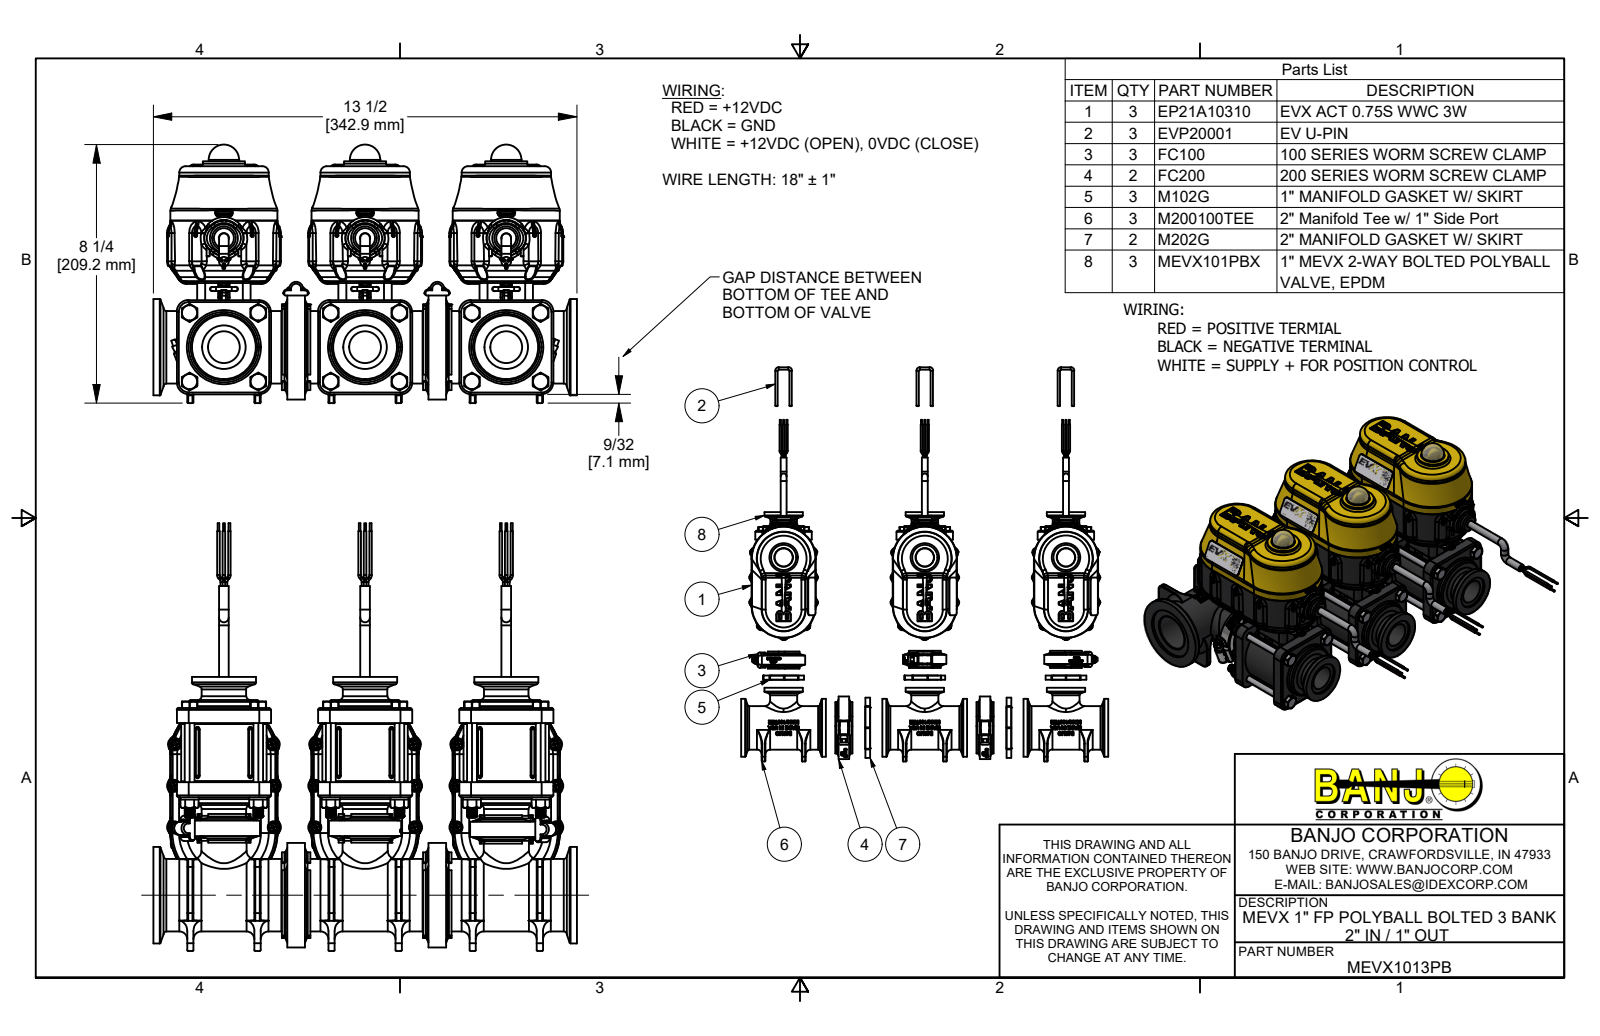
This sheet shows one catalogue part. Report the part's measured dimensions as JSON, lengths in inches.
{"part_name": "MEVX1013PB; EP21A10310; EP10310; IRF4905 (+8 more)", "step_written_by": "Autodesk Inventor 2022 (AUTOMOTIVE_DESIGN)", "units": "inches", "bodies": {"solids": 301, "faces": 38096, "planar": 9844, "cylindrical": 11223, "other": 17029}, "overall_size": [13.627, 13.5, 8.237], "volume_in3": 207.9, "surface_area_in2": 2243, "round_holes": [[0.095, 33], [0.15, 33], [0.08, 21], [0.107, 12], [0.126, 12], [0.136, 12], [0.148, 12], [0.15, 12], [0.17, 12], [0.252, 12], [0.322, 12], [0.36, 12]], "round_bosses_or_shafts": [[0.268, 180], [0.25, 51], [0.08, 45], [0.14, 33], [0.108, 33], [0.085, 33], [0.058, 18], [0.313, 15]], "partial_cylinders_radius": [[0.013, 540], [0.04, 435], [0.01, 277], [0.02, 242], [0.03, 235], [0.005, 143], [0.06, 114], [0.015, 89]], "face_to_face_distances": [4.5, 0.1, 2.565, 0.48, 9, 0.06, 0.211, 0.151, 2.365, 0.995], "hole_center_spacings": [4.5, 1.662, 1.891, 2.656, 2.69, 2.715, 3.366, 4.509]}
